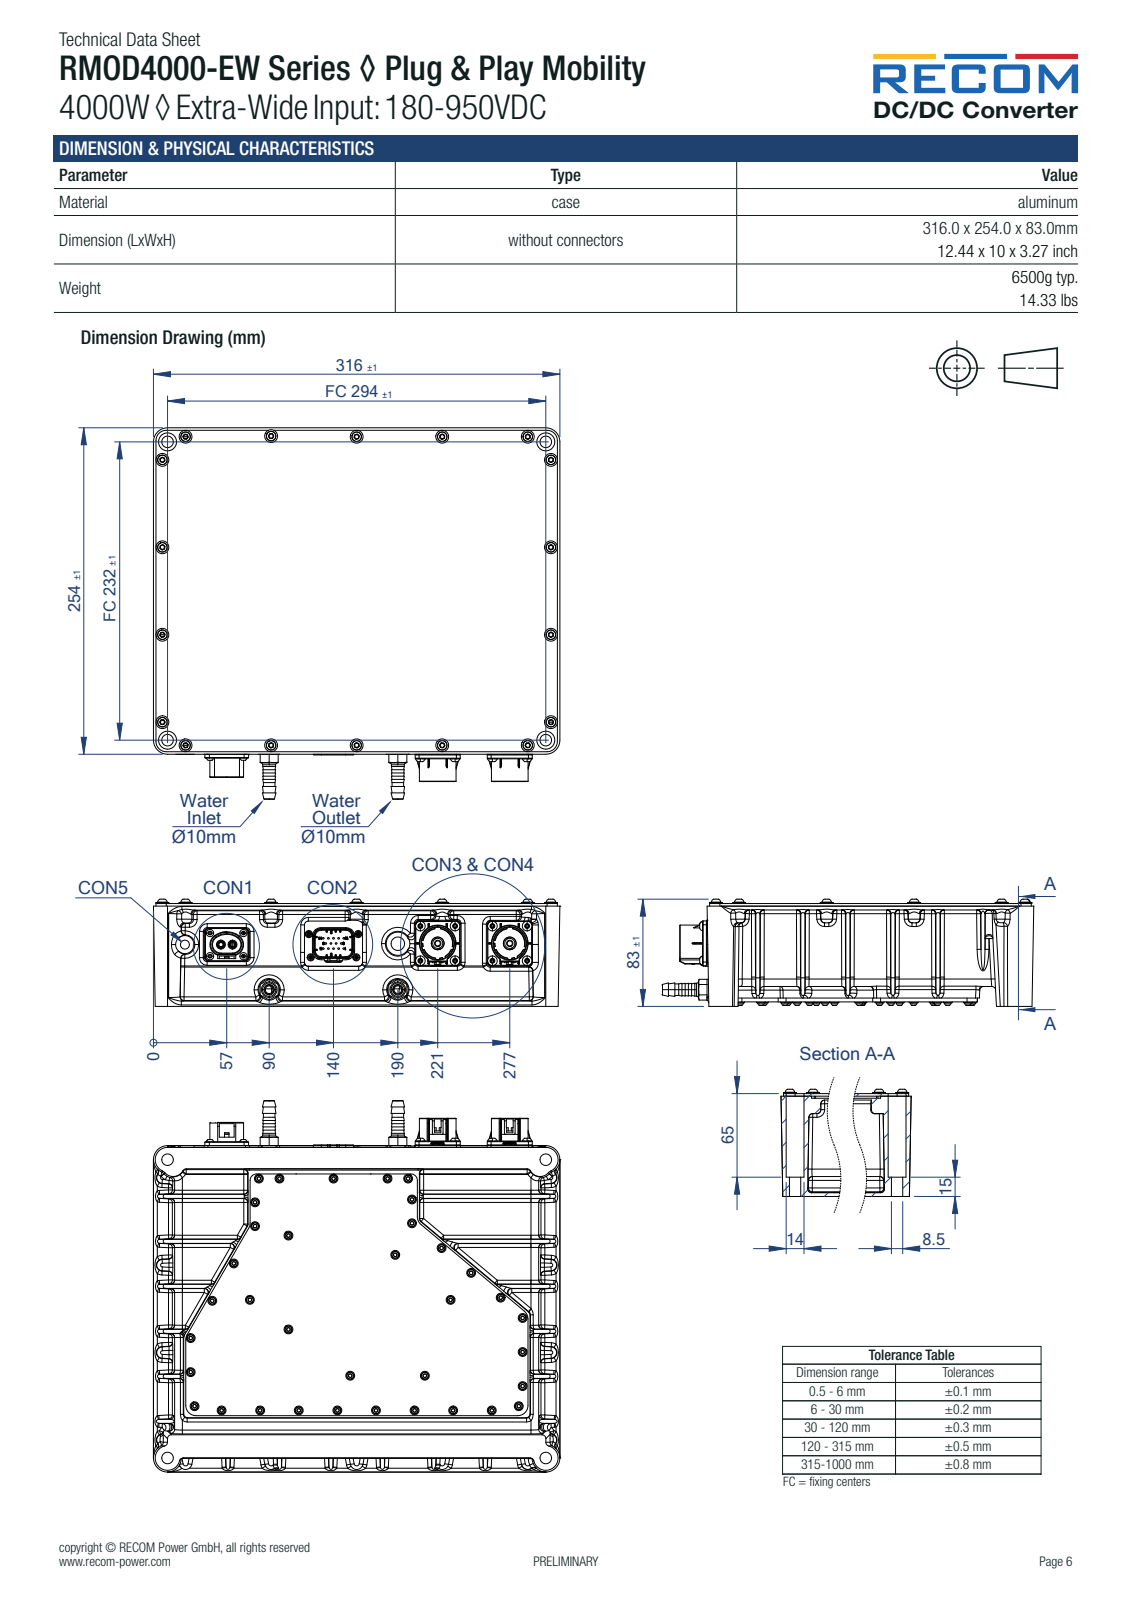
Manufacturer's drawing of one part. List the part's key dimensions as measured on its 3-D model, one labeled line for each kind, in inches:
Part name (STEP PRODUCT): 13950183; ME1110; VITE ISO 7380 FLANGIATA INOX A2 M3X6 TORX T10; RMOD4000_final 231123 (+1 more)
STEP written by: SolidWorks 2022 (AUTOMOTIVE_DESIGN)
Units: inches
Bodies: 81 solids, 6674 faces (2591 planar, 1919 cylindrical, 2164 other)
Overall size (bounding box): 12.437 × 11.376 × 3.283
Volume: 85.68 in³ · Surface area: 1 125 in²
Round holes (diameter × count): ⌀0.098 ×56, ⌀0.138 ×35, ⌀0.13 ×26, ⌀0.177 ×18, ⌀0.161 ×8, ⌀0.165 ×8, ⌀0.085 ×4, ⌀0.118 ×4, ⌀0.126 ×4, ⌀0.354 ×4, ⌀0.551 ×4, ⌀0.128 ×2
Round bosses / shafts (diameter × count): ⌀0.118 ×40, ⌀0.272 ×36, ⌀0.051 ×28, ⌀0.157 ×26, ⌀0.394 ×22, ⌀0.276 ×7, ⌀0.236 ×4, ⌀0.22 ×4
Partial cylindrical surfaces — rounded edges, fillets, slot ends (radius × count): R0.118 ×441, R0.016 ×108, R0.027 ×108, R0.039 ×57, R0.02 ×52, R0.059 ×42, R0.079 ×31, R0.197 ×29
Main face-to-face distances: 0.079, 2.815, 2.894, 0.138, 0.61, 0.118, 0.492, 2.402, 2.933, 3.012
Hole centre spacings: 0.752, 1.063, 2.205, 2.677, 12.187, 2.618, 0.745, 0.759
